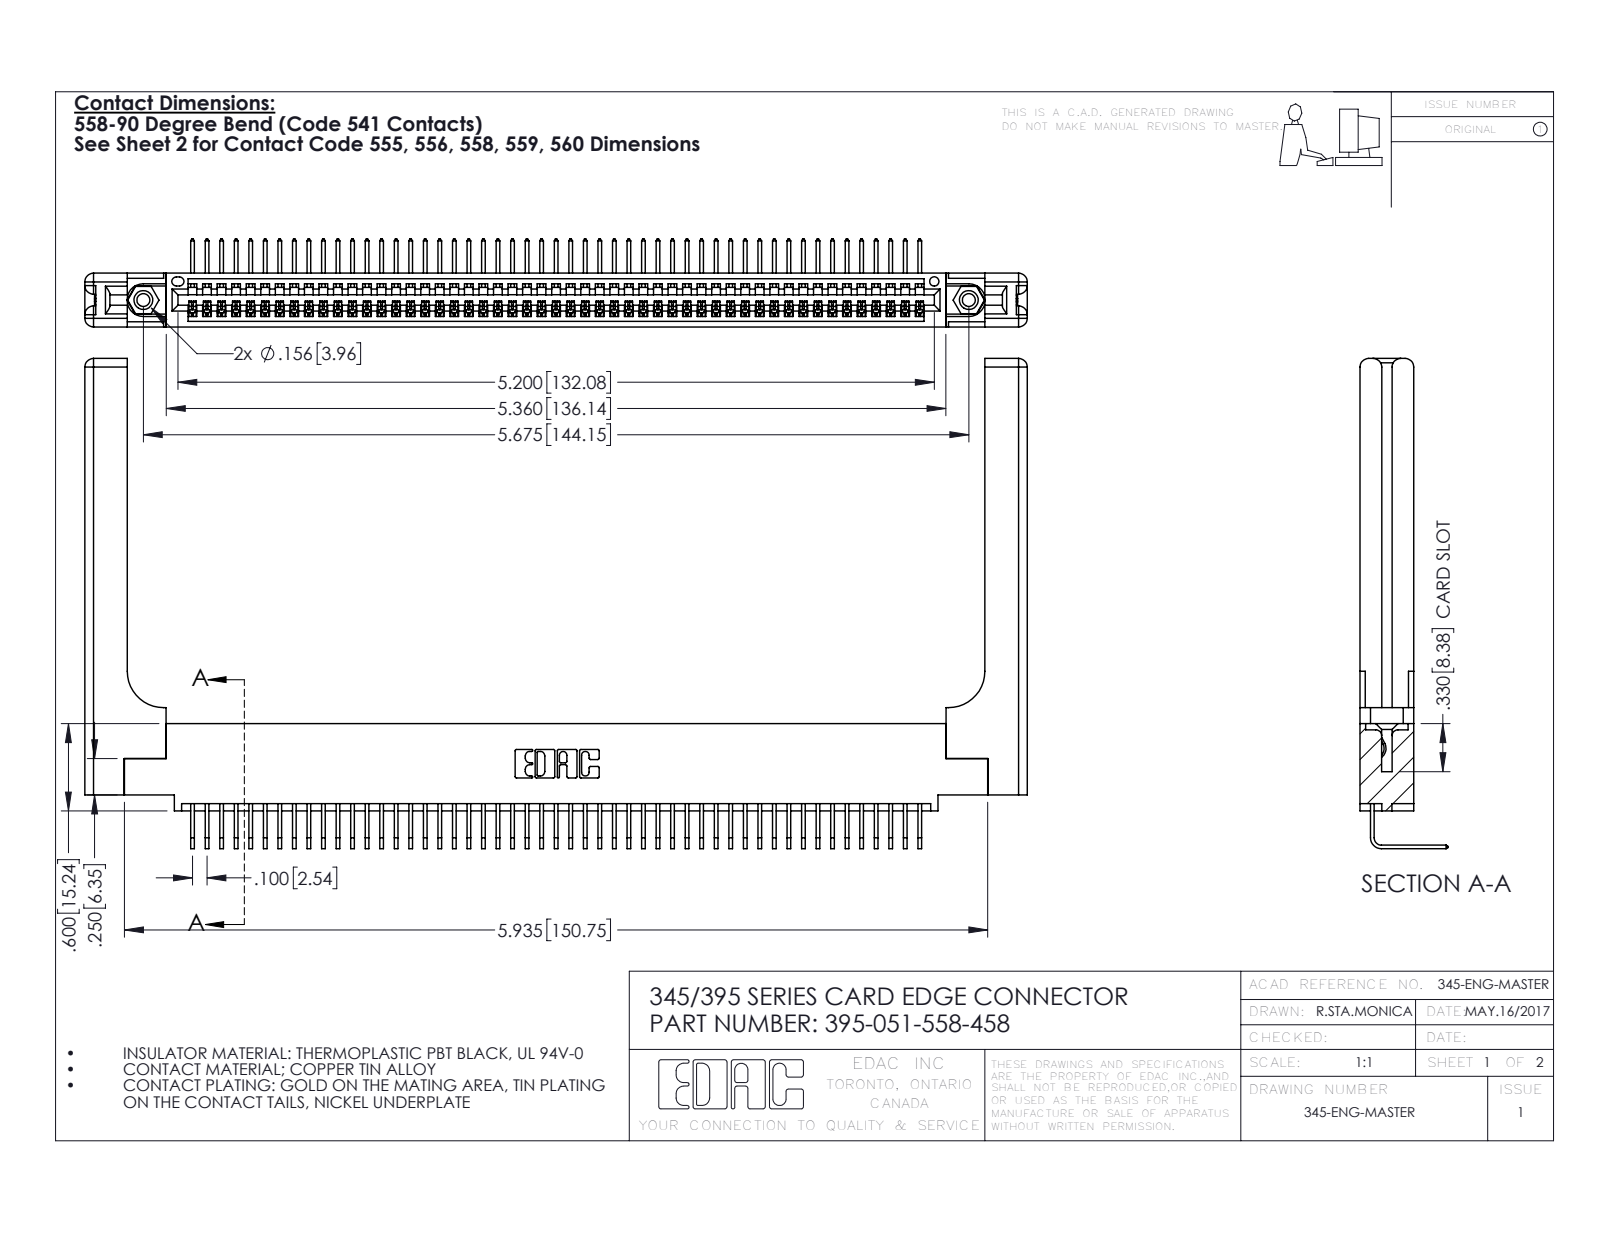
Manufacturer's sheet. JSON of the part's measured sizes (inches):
{"part_name": "345-250-001_345-250-001-102; 395-051-558-458; 345 Part_0.110 Offset - 0.156 Dia-TH; 345-220-058_345-220-058 (+1 more)", "step_written_by": "SolidWorks 2016 (CONFIG_CONTROL_DESIGN)", "units": "inches", "bodies": {"solids": 56, "faces": 3446, "planar": 2374, "cylindrical": 1012, "other": 60}, "overall_size": [6.479, 3.369, 0.605], "volume_in3": 1.483, "surface_area_in2": 42.63, "round_holes": [[0.089, 2], [0.125, 2], [0.156, 2], [0.064, 1]], "round_bosses_or_shafts": [[0.155, 2]], "partial_cylinders_radius": [[0.006, 102], [0.01, 22], [0.06, 16], [0.007, 6], [0.031, 6], [0.026, 3], [0.03, 2], [0.031, 2]], "face_to_face_distances": [0.072, 0.37, 0.298, 0.098, 0.272, 0.025, 0.2, 0.225, 0.148, 0.15], "hole_center_spacings": [0.27, 5.439, 5.675]}
